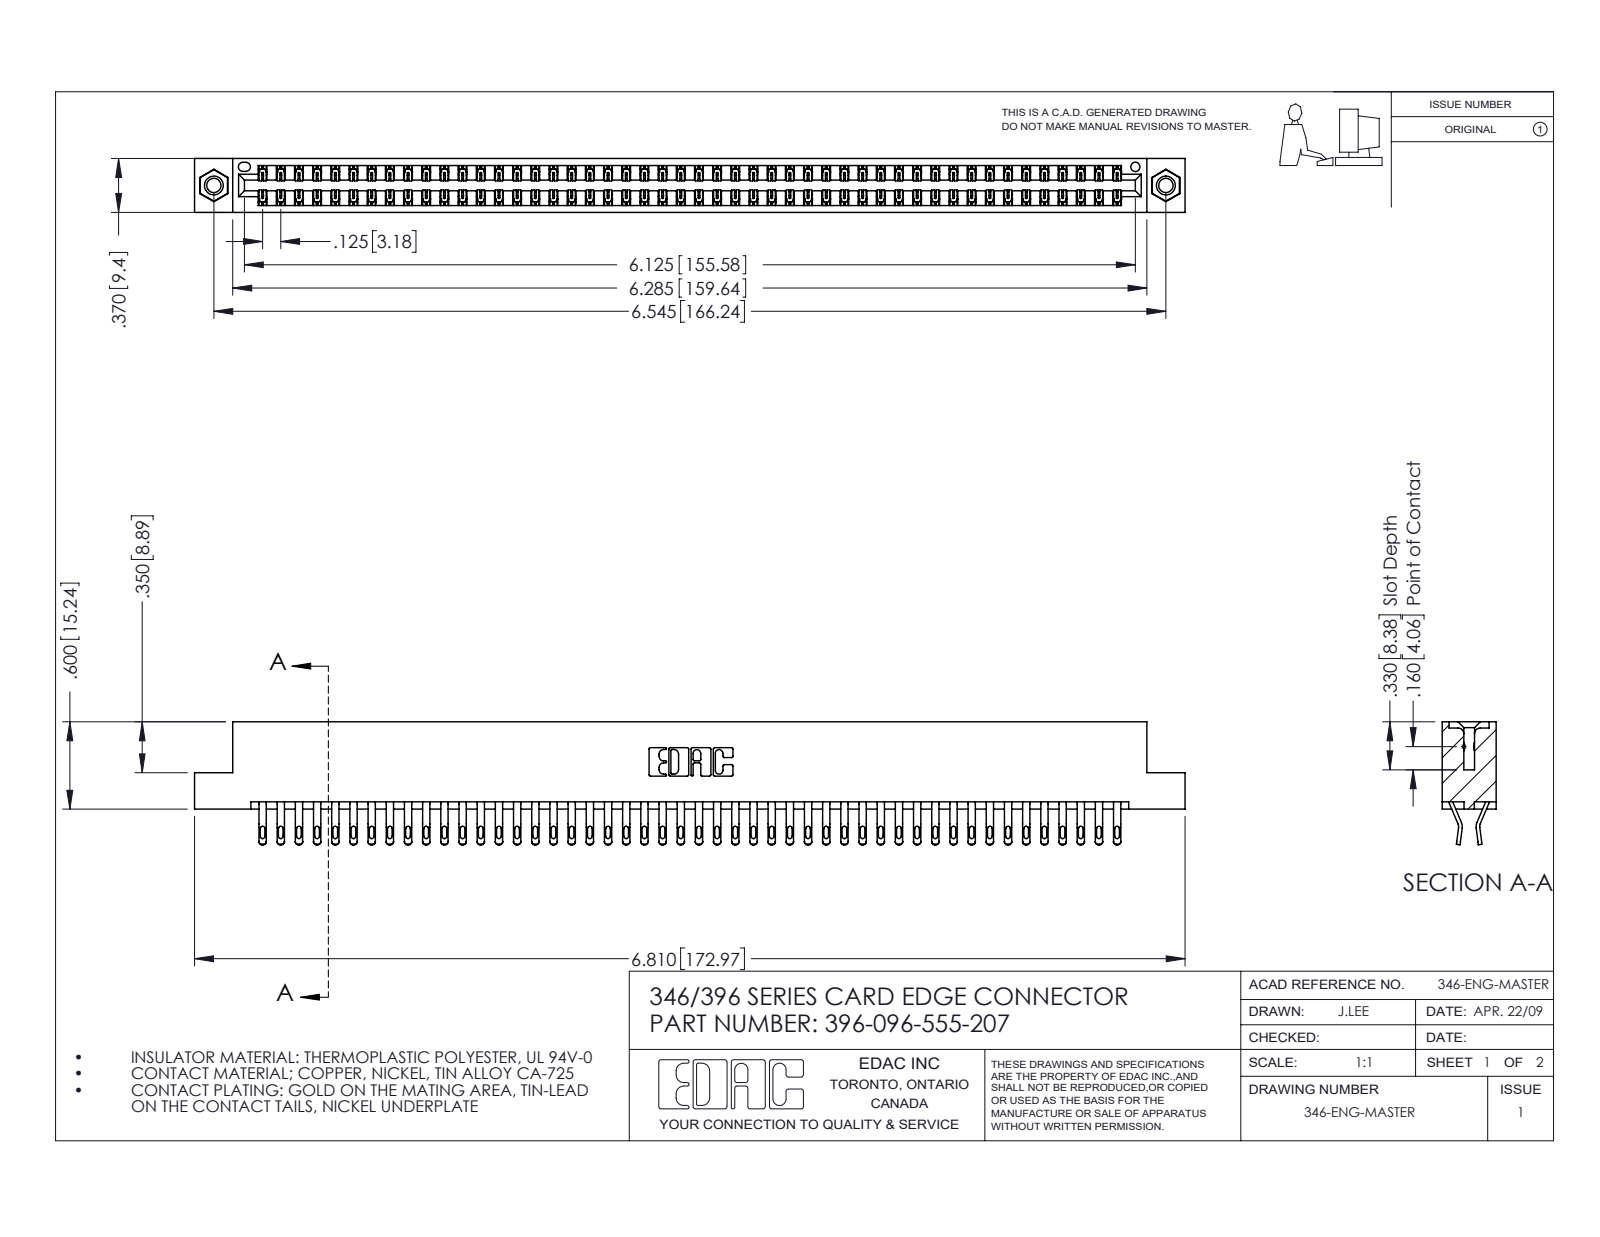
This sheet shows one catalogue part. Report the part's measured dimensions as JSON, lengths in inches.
{"part_name": "345-250-001_345-250-005-103; 345-292-001_555 Tail; 346 Part_Flush Mounting Lugs - 0.156 Dia-TI; 396-096-555-207", "step_written_by": "SolidWorks 2016 (CONFIG_CONTROL_DESIGN)", "units": "inches", "bodies": {"solids": 99, "faces": 5750, "planar": 3276, "cylindrical": 2458, "other": 16}, "overall_size": [6.81, 0.845, 0.37], "volume_in3": 1.048, "surface_area_in2": 38.34, "round_holes": [[0.098, 2], [0.125, 2], [0.156, 2], [0.064, 1]], "round_bosses_or_shafts": [[0.155, 2]], "partial_cylinders_radius": [[0.016, 192], [0.02, 192], [0.006, 144], [0.01, 22], [0.007, 6], [0.031, 6], [0.026, 3], [0.01, 2]], "face_to_face_distances": [0.048, 0.322, 0.37, 0.25, 0.025, 0.072, 0.298, 0.275, 0.148, 0.222], "hole_center_spacings": [0.246, 6.336, 6.545]}
